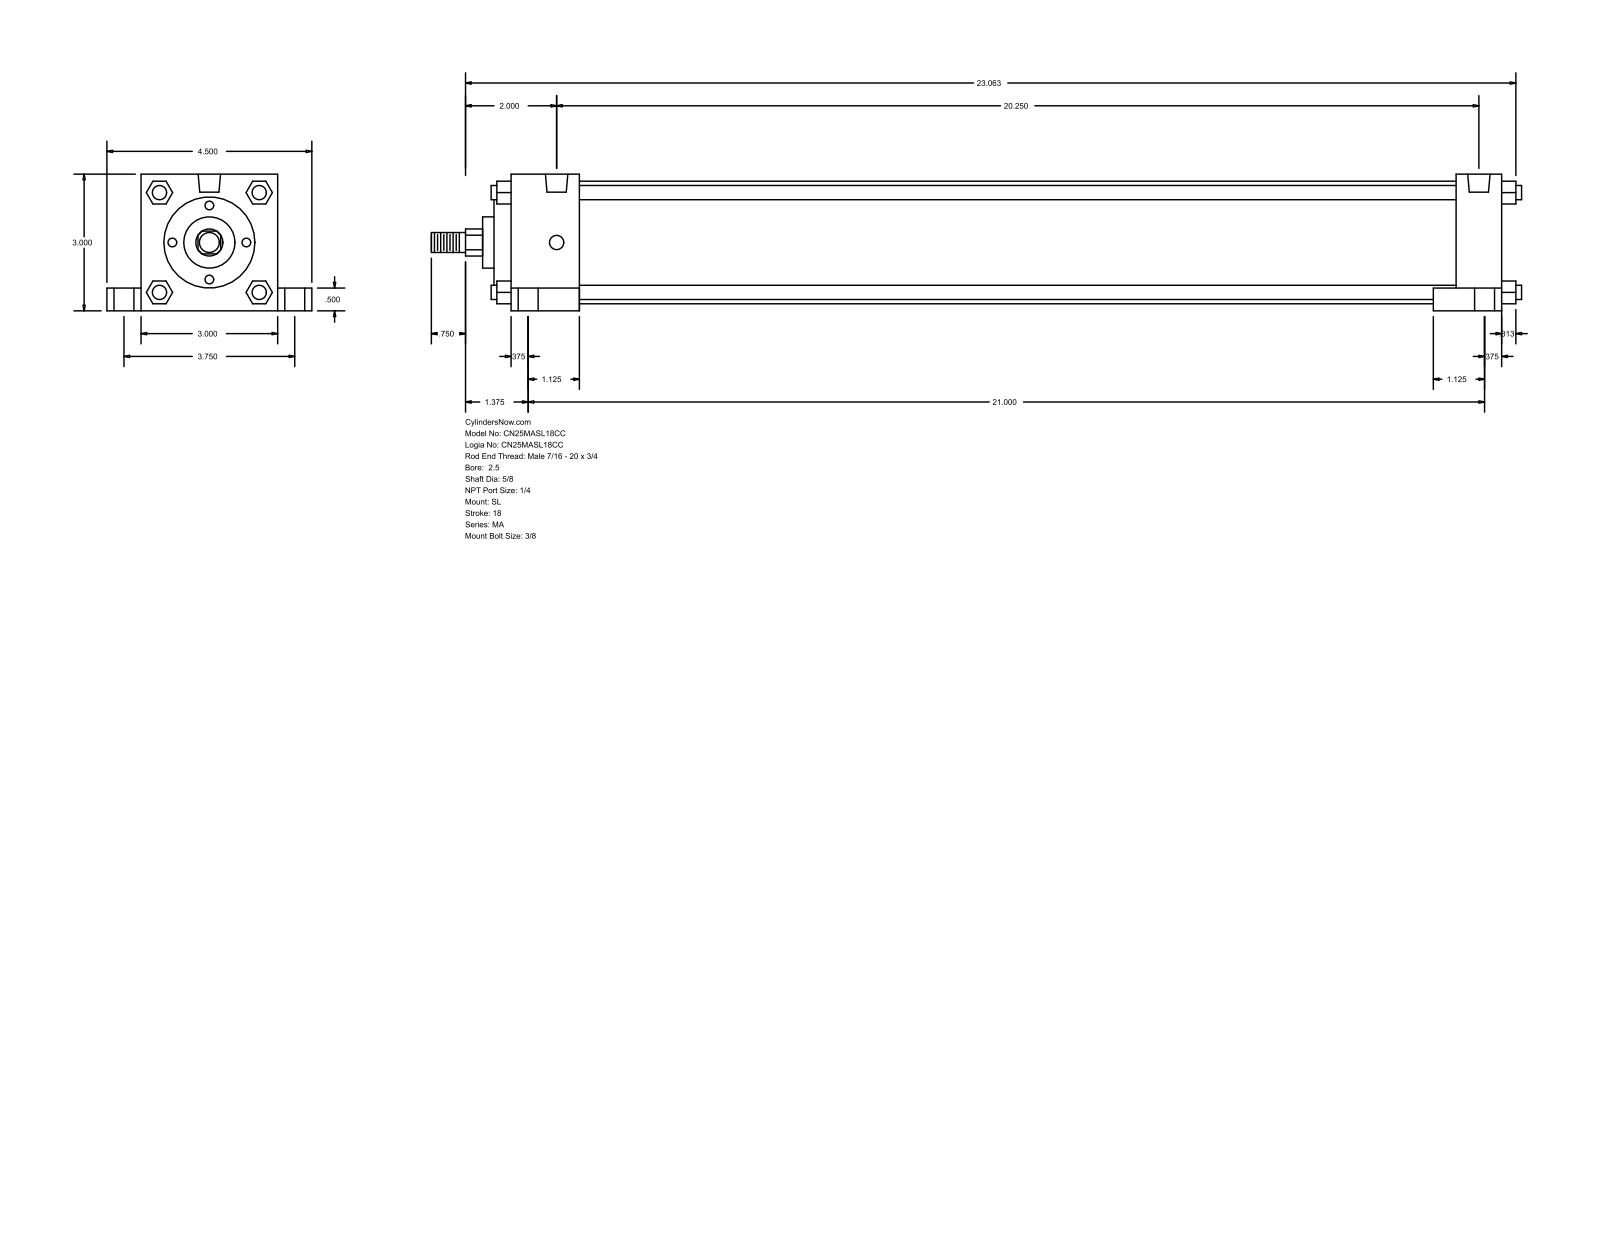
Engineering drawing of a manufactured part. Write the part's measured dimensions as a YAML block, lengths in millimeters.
part_name: "MA_SL__0250_0.625"
step_written_by: "GSSL Pune (CONFIG_CONTROL_DESIGN)"
units: millimeters
bodies: {solids: 0, faces: 150, planar: 113, cylindrical: 37, other: 0}
overall_size: [608.01, 114.3, 76.2]
round_holes:
  - {diameter: 7.94, count: 4}
  - {diameter: 11.11, count: 4}
  - {diameter: 17.46, count: 4}
  - {diameter: 12.49, count: 2}
round_bosses_or_shafts:
  - {diameter: 7.94, count: 4}
  - {diameter: 68.33, count: 1}
  - {diameter: 50.8, count: 1}
  - {diameter: 28.57, count: 1}
  - {diameter: 15.88, count: 1}
  - {diameter: 11.11, count: 1}
partial_cylinders:
  - {radius: 7.54, count: 1}
face_to_face_distances: [76.2, 552.45, 12.7, 488.95, 25.4, 38.1, 514.35, 527.05, 19.05, 63.5]
hole_center_spacings: [47.73, 50.2, 95.24, 514.35, 519.72, 532.36, 533.41, 541.85]
